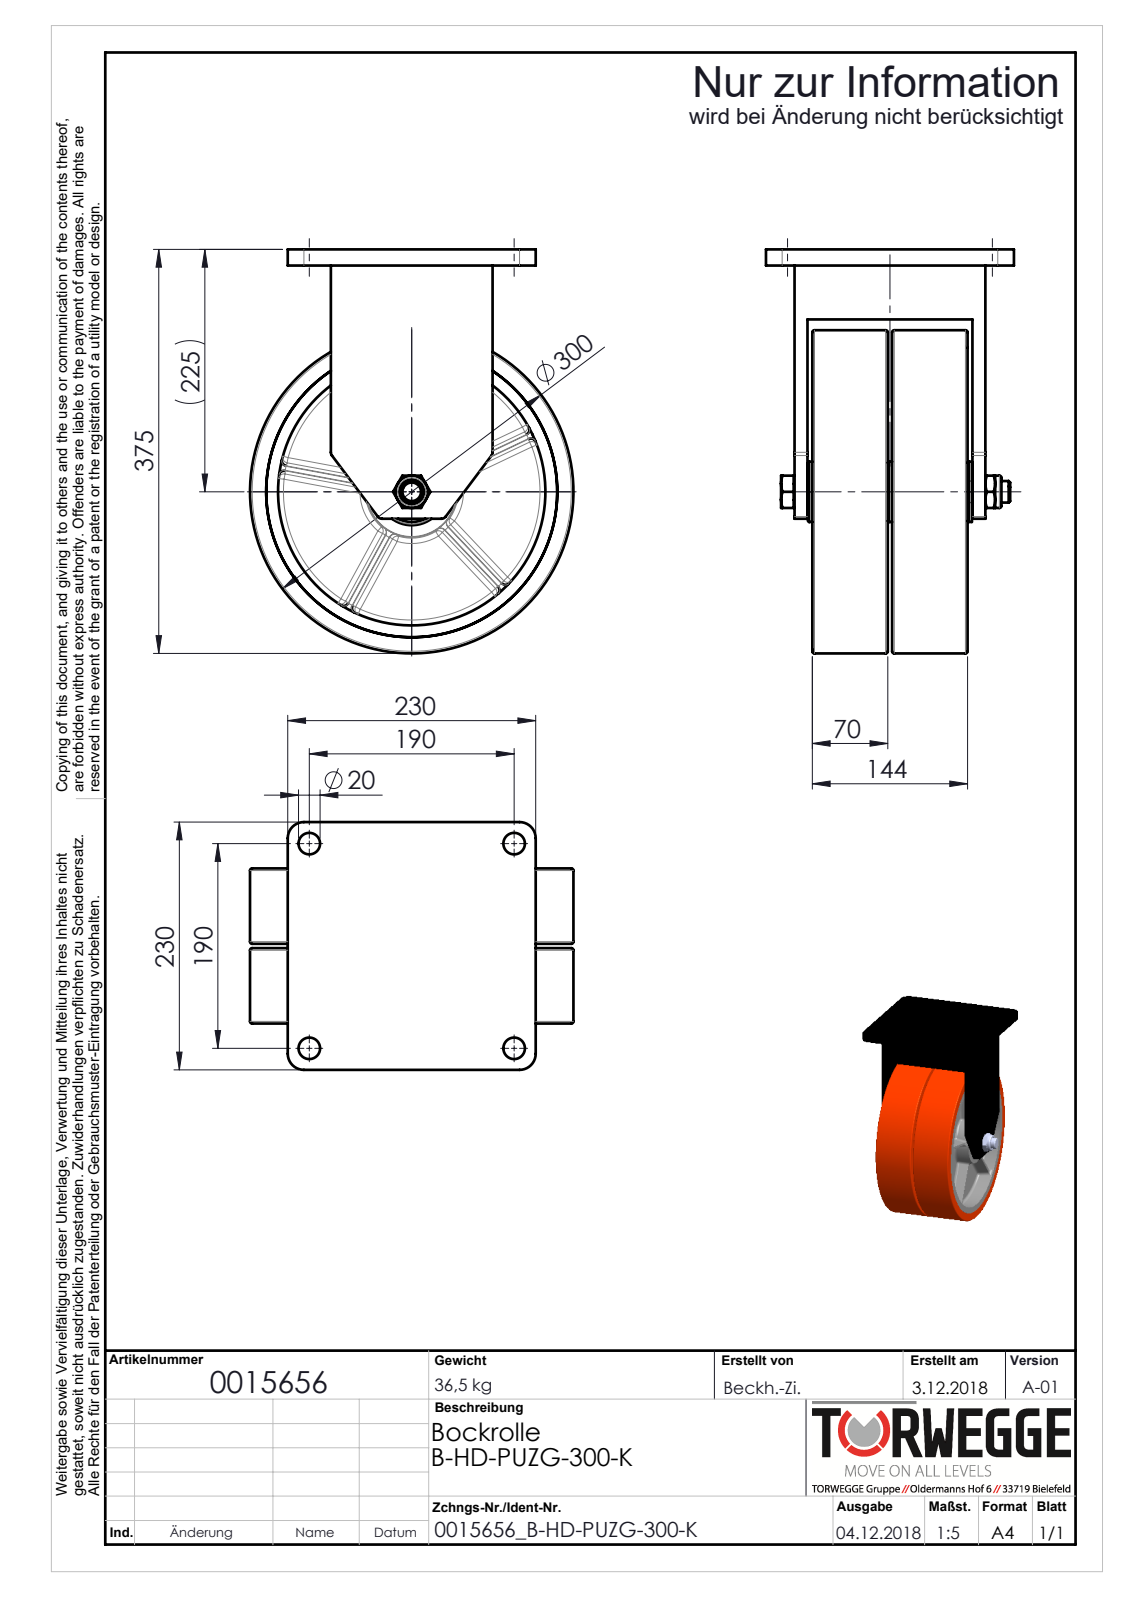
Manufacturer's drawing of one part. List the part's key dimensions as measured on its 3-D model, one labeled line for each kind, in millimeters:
Part name (STEP PRODUCT): 0015656_B-HD-PUZG-300-K_(A-01)
STEP written by: SolidWorks 2018 (AUTOMOTIVE_DESIGN)
Units: millimetres
Bodies: 34 solids, 1037 faces (205 planar, 288 cylindrical, 544 other)
Overall size (bounding box): 375 × 300 × 230
Volume: 7 072 000 mm³ · Surface area: 1 287 000 mm²
Round holes (diameter × count): ⌀20 ×5, ⌀17.5 ×1, ⌀20.2 ×1, ⌀21 ×1, ⌀22.86 ×1, ⌀25.2 ×1, ⌀30 ×1, ⌀30.2 ×1, ⌀31 ×1, ⌀38.48 ×1, ⌀51.57 ×1, ⌀53.52 ×1
Round bosses / shafts (diameter × count): ⌀300 ×1, ⌀56 ×1, ⌀40.43 ×1, ⌀35 ×1, ⌀25 ×1
Partial cylindrical surfaces — rounded edges, fillets, slot ends (radius × count): R5 ×44, R0.5 ×40, R15 ×4
Main face-to-face distances: 74, 28, 42, 12, 58.5, 106.5, 32.5, 132.5, 165, 118.5
Hole centre spacings: 190, 268.7
